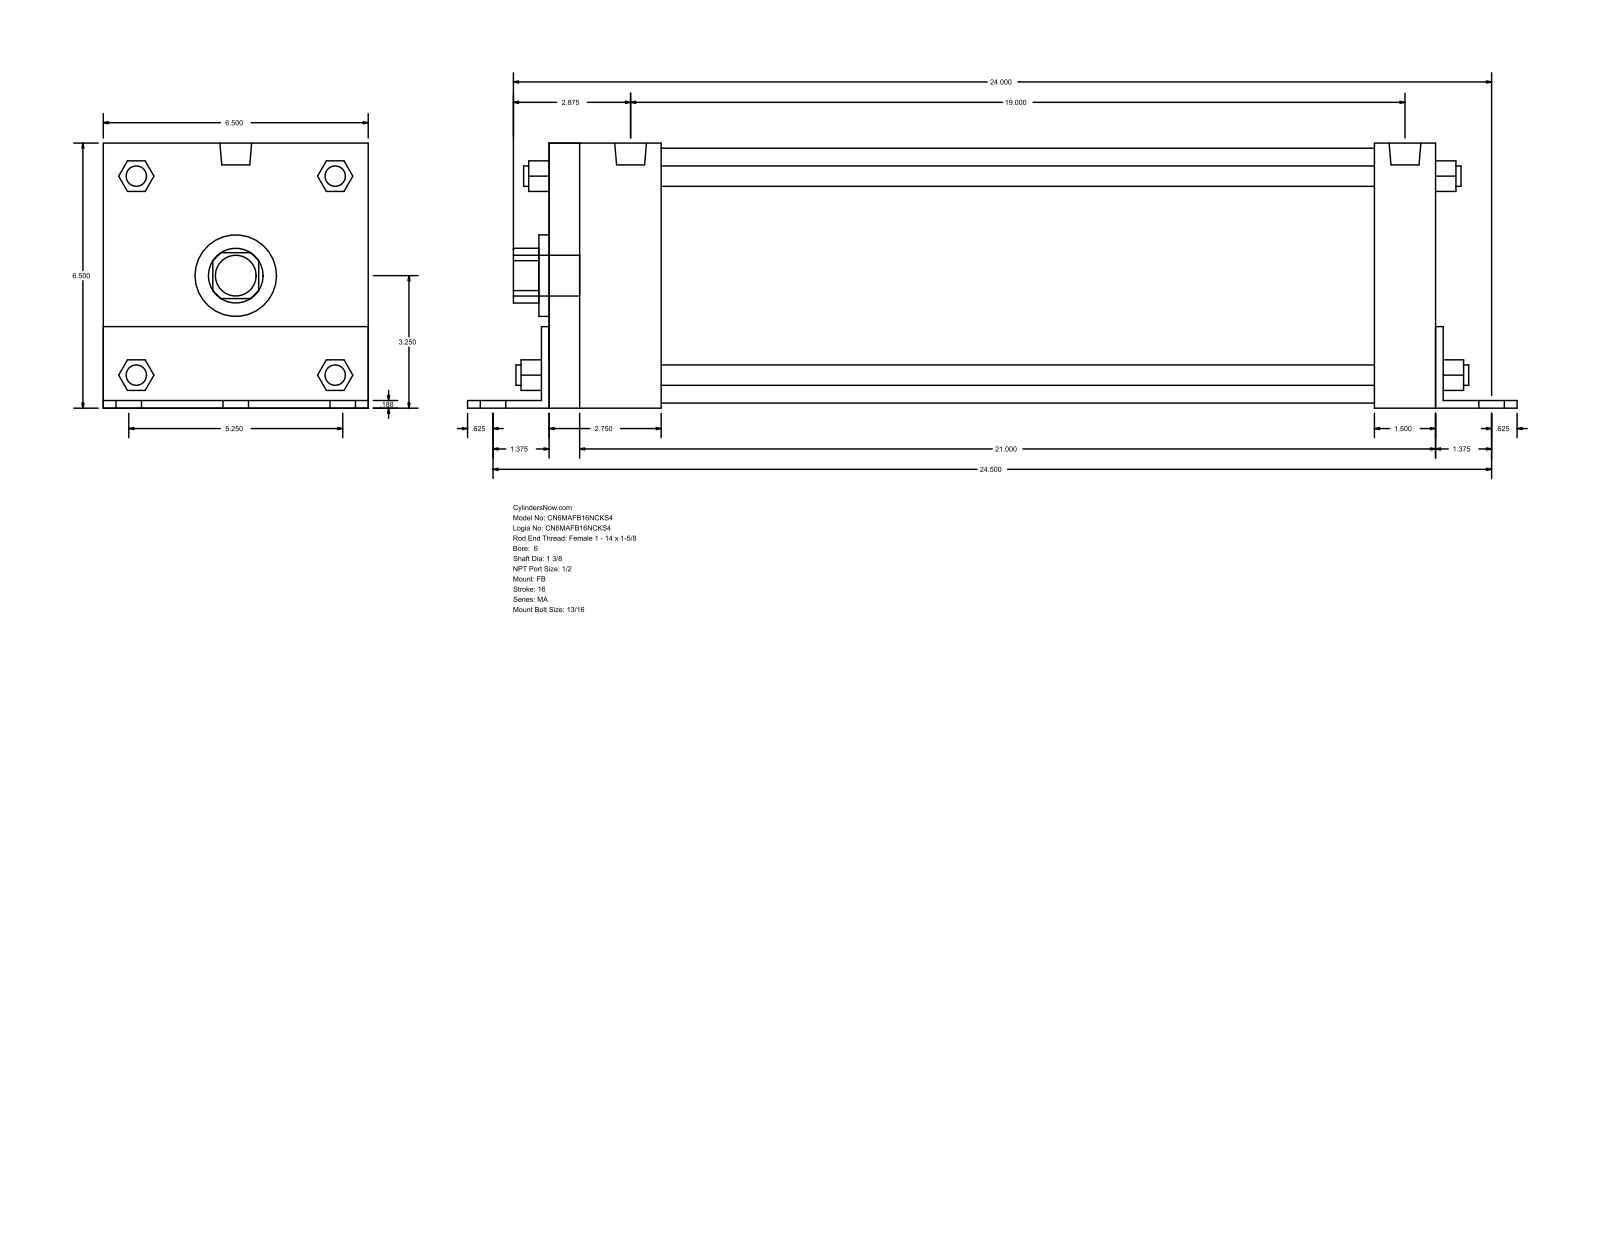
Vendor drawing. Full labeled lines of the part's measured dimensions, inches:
Part name (STEP PRODUCT): MA_FB__0600_1.375
STEP written by: GSSL Pune (CONFIG_CONTROL_DESIGN)
Units: inches
Bodies: 0 solids, 140 faces (105 planar, 35 cylindrical, 0 other)
Overall size (bounding box): 25.625 × 6.502 × 6.5
Round holes (diameter × count): ⌀1.375 ×1, ⌀2 ×1, ⌀6.25 ×1
Round bosses / shafts (diameter × count): ⌀0.813 ×6, ⌀0.687 ×4, ⌀0.5 ×4, ⌀0.778 ×2, ⌀1 ×1
Partial cylindrical surfaces — rounded edges, fillets, slot ends (radius × count): R0.672 ×1, R1.262 ×1
Main face-to-face distances: 6.5, 0.187, 21.625, 6.502, 0.185, 6.315, 0.188, 1.5, 21.813, 22
